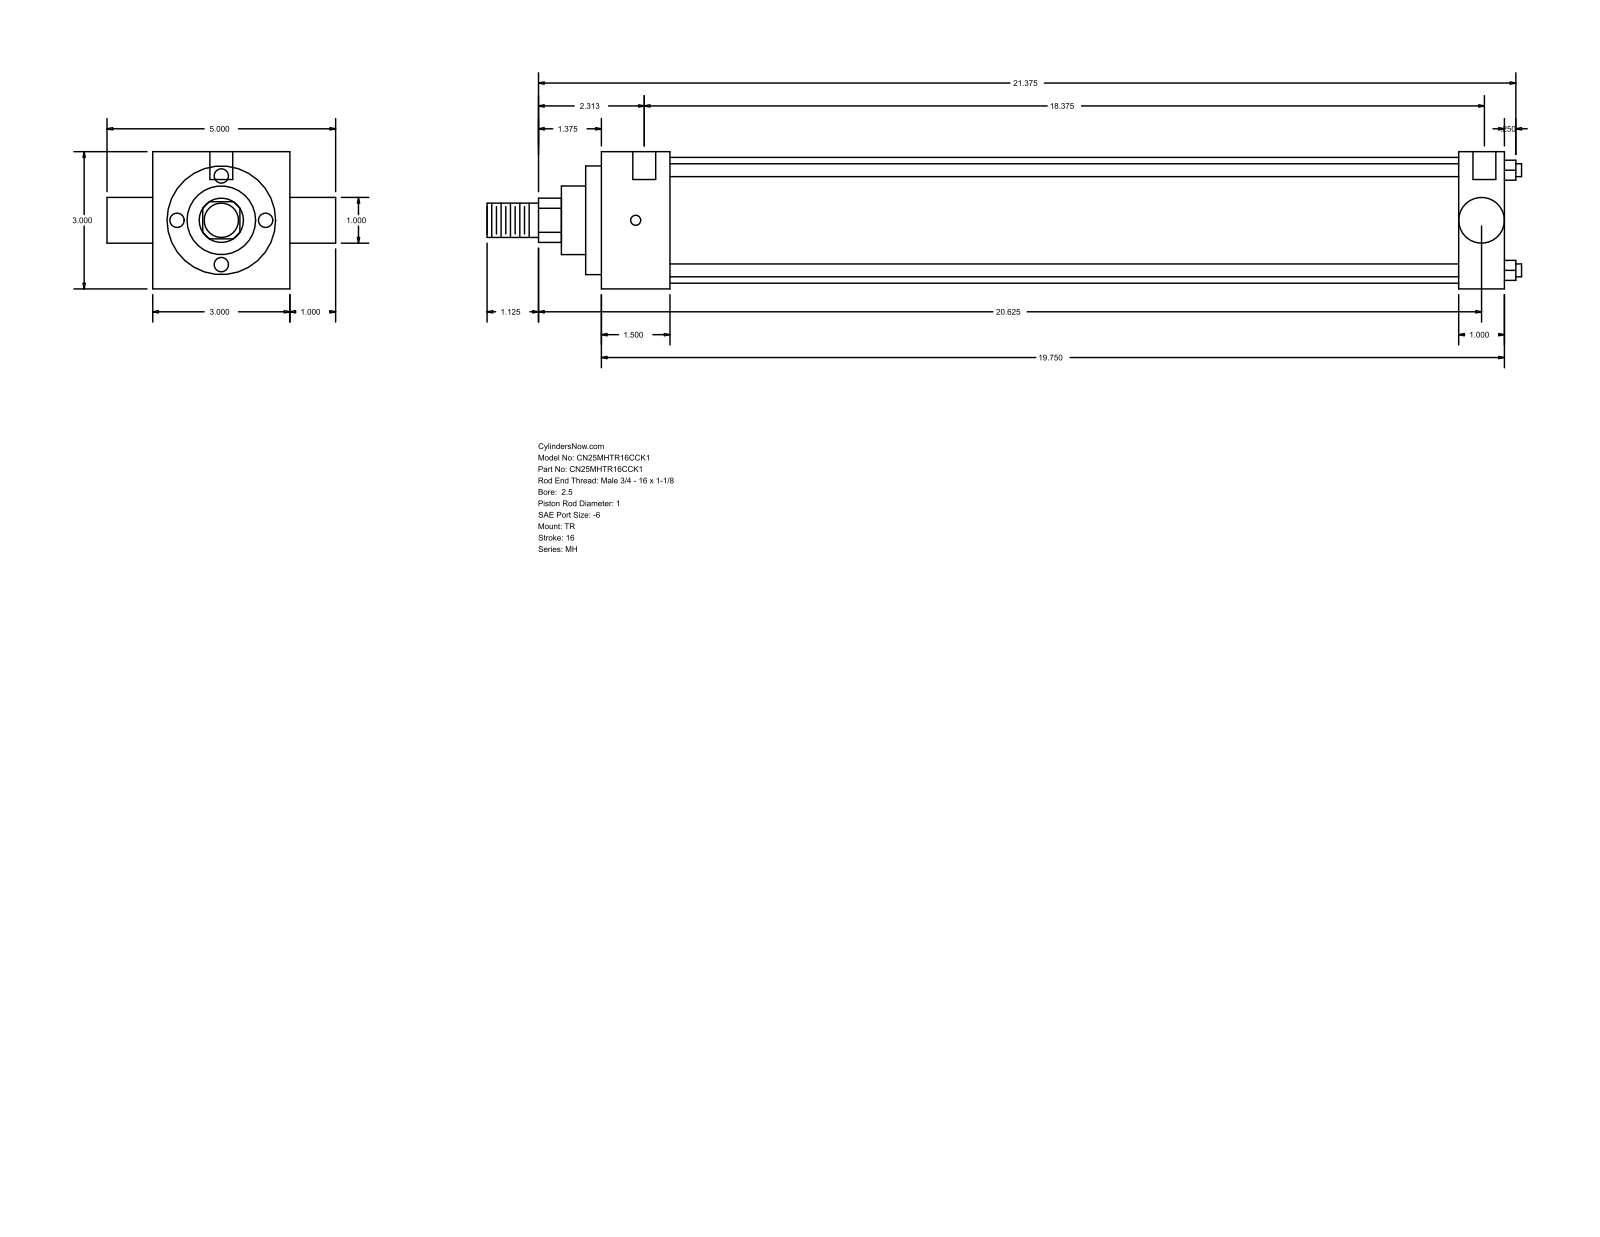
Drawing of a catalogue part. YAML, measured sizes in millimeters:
part_name: "MH_TR__0250_1"
step_written_by: "GSSL Pune (CONFIG_CONTROL_DESIGN)"
units: millimeters
bodies: {solids: 0, faces: 86, planar: 61, cylindrical: 25, other: 0}
overall_size: [574.67, 127, 76.2]
round_holes:
  - {diameter: 5.56, count: 3}
  - {diameter: 12.7, count: 2}
round_bosses_or_shafts:
  - {diameter: 7.14, count: 4}
  - {diameter: 69.85, count: 1}
  - {diameter: 60.33, count: 1}
  - {diameter: 38.1, count: 1}
  - {diameter: 25.4, count: 1}
  - {diameter: 25.35, count: 1}
  - {diameter: 19.05, count: 1}
partial_cylinders:
  - {radius: 12.29, count: 1}
face_to_face_distances: [76.2, 501.66, 25.4, 38.11, 463.55, 476.26, 438.15, 8.73, 46.84, 484.99]
hole_center_spacings: [3.18, 4.76, 466.72, 469.9, 471.48, 474.66]
